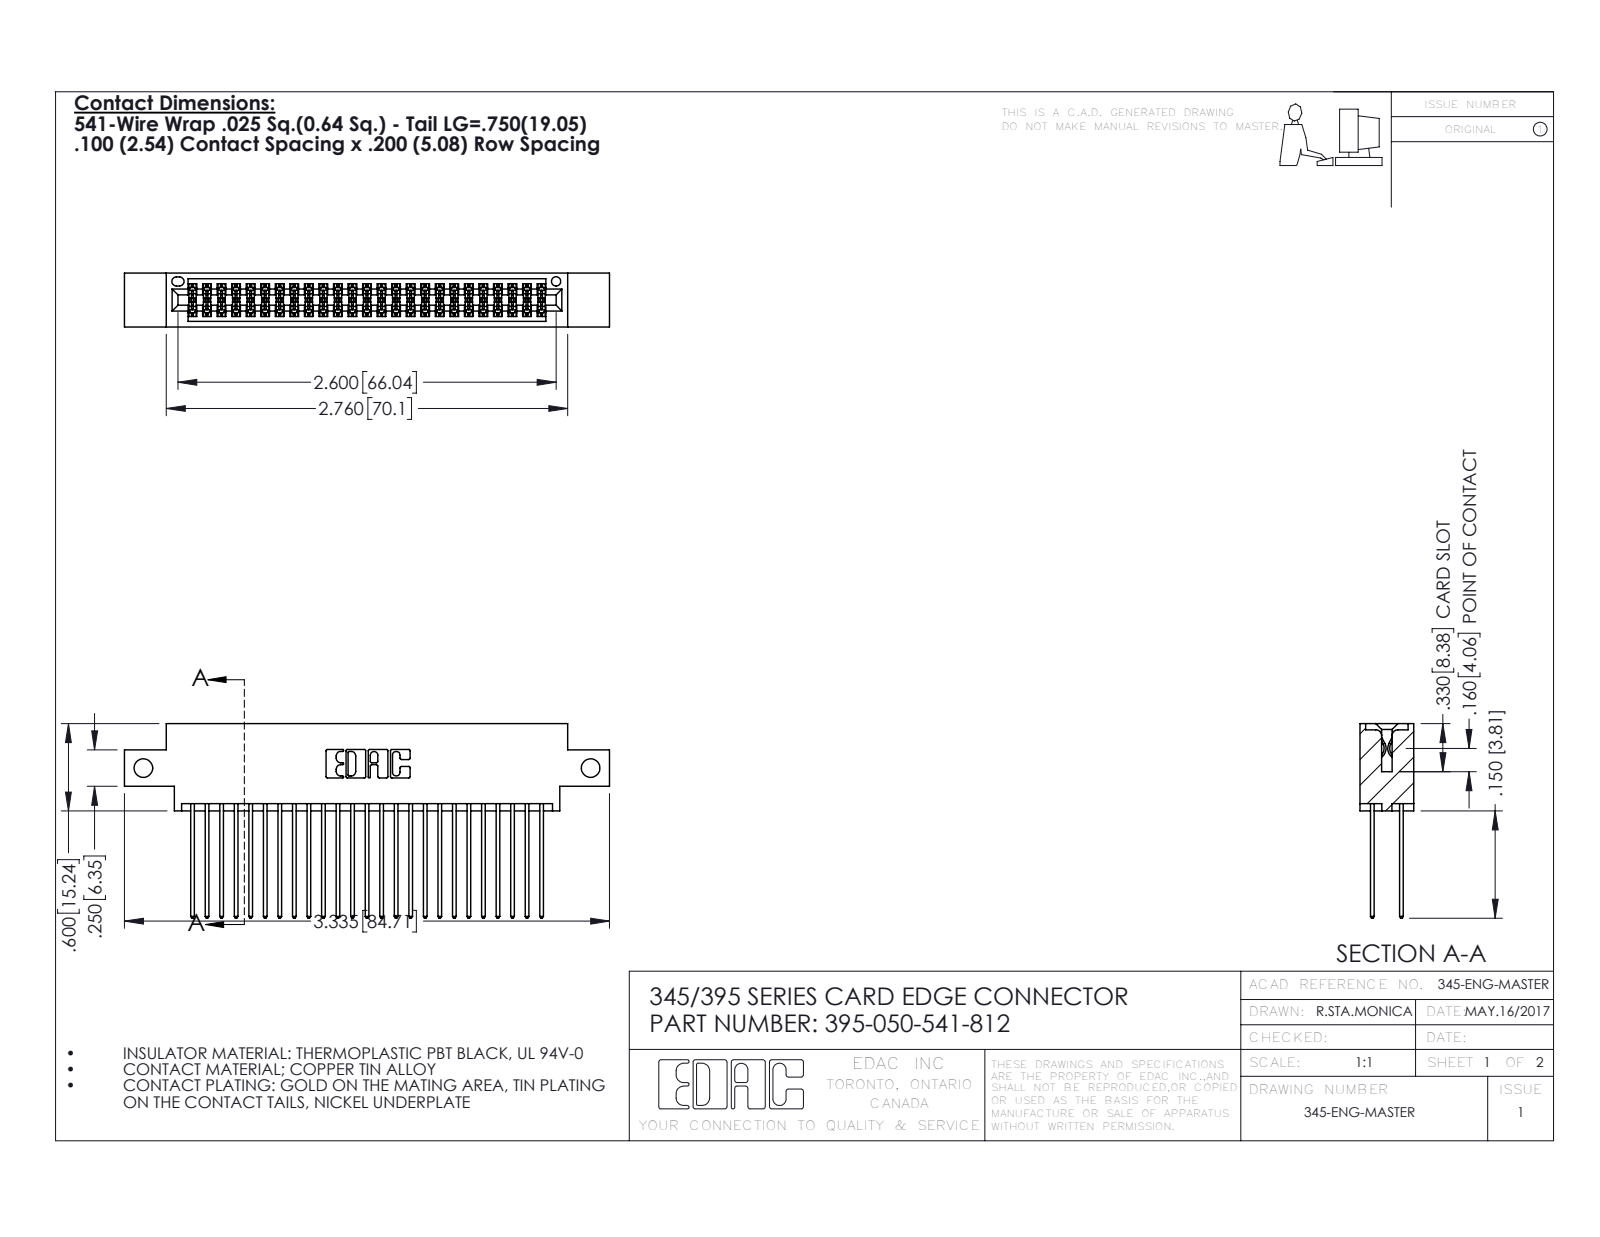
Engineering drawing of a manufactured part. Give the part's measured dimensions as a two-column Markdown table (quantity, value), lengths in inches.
| quantity | value |
| --- | --- |
| part name | 395-050-541-812; 345-292-001_345-293-141; 345 Part_0.170 Offset - Side Mount |
| STEP written by | SolidWorks 2016 (CONFIG_CONTROL_DESIGN) |
| units | inches |
| bodies | 51 solids, 2630 faces (1734 planar, 896 cylindrical, 0 other) |
| overall size | 3.335 × 1.337 × 0.37 |
| volume | 0.498 in³ |
| surface area | 20.28 in² |
| round holes (diameter × count) | 0.128 × 2, 0.064 × 1 |
| partial cylindrical surfaces (radius × count) | 0.006 × 75, 0.01 × 50, 0.01 × 22, 0.007 × 6, 0.031 × 6, 0.026 × 3, 0.014 × 2, 0.019 × 2 |
| main face-to-face distances | 0.072, 0.298, 0.2, 0.098, 0.272, 0.025, 0.37, 0.225, 0.175, 0.149 |
| hole center spacings | 3.075 |
